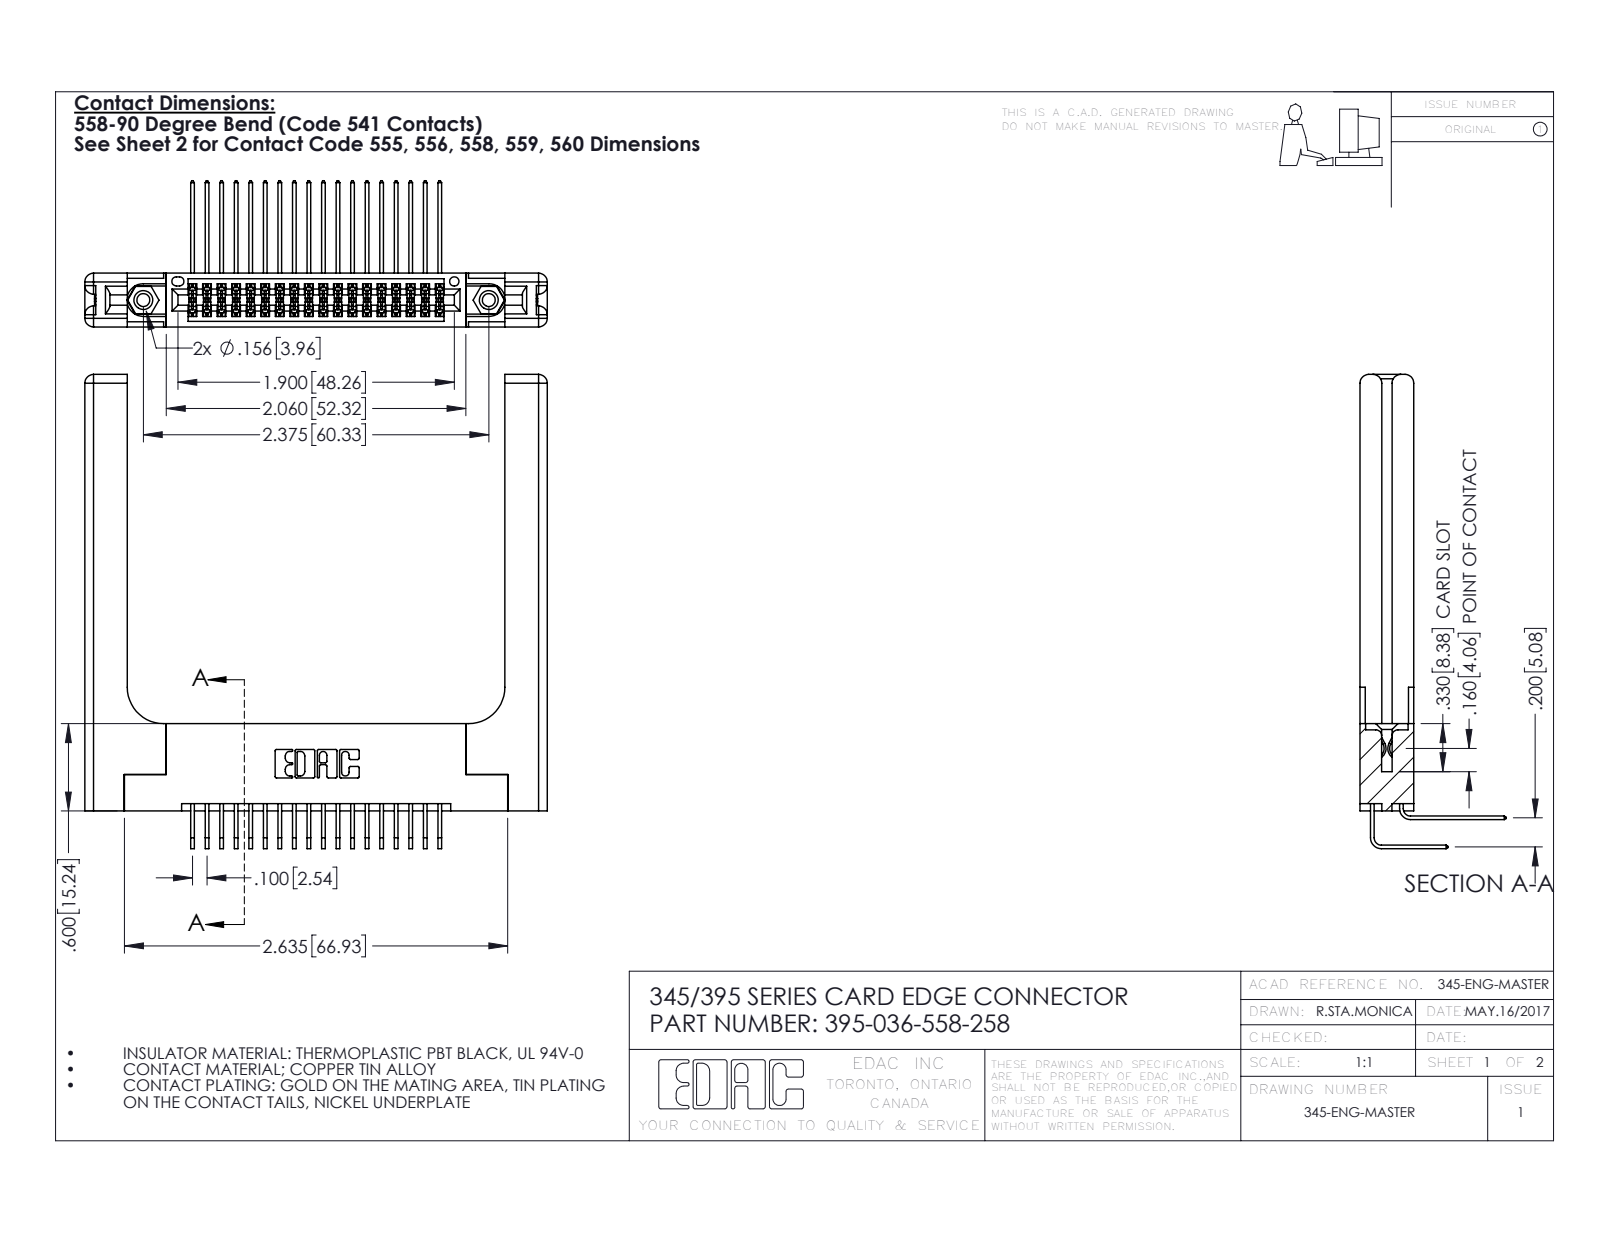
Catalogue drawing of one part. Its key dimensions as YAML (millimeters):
part_name: "345 Part_Flush Mounting Lugs - 0.156 Dia-TH; 345-250-001_345-250-001-102; 345-292-001_558 559 Tail - 1; 345-220-058_345-220-058 (+2 more)"
step_written_by: "SolidWorks 2016 (CONFIG_CONTROL_DESIGN)"
units: millimeters
bodies: {solids: 41, faces: 2254, planar: 1488, cylindrical: 706, other: 60}
overall_size: [82.8, 80.7, 25.5]
volume: 16300
surface_area: 17140
round_holes:
  - {diameter: 2.3, count: 2}
  - {diameter: 3.2, count: 2}
  - {diameter: 4, count: 2}
  - {diameter: 1.6, count: 1}
round_bosses_or_shafts:
  - {diameter: 3.9, count: 2}
partial_cylinders:
  - {radius: 0.2, count: 55}
  - {radius: 0.3, count: 22}
  - {radius: 1.5, count: 16}
  - {radius: 0.2, count: 6}
  - {radius: 0.8, count: 6}
  - {radius: 0.7, count: 3}
  - {radius: 0.4, count: 2}
  - {radius: 0.5, count: 2}
face_to_face_distances: [9.4, 1.8, 7.6, 5.1, 3.8, 3.8, 2, 5.6, 2.5, 6.9]
hole_center_spacings: [6.9, 54.4, 60.3]
